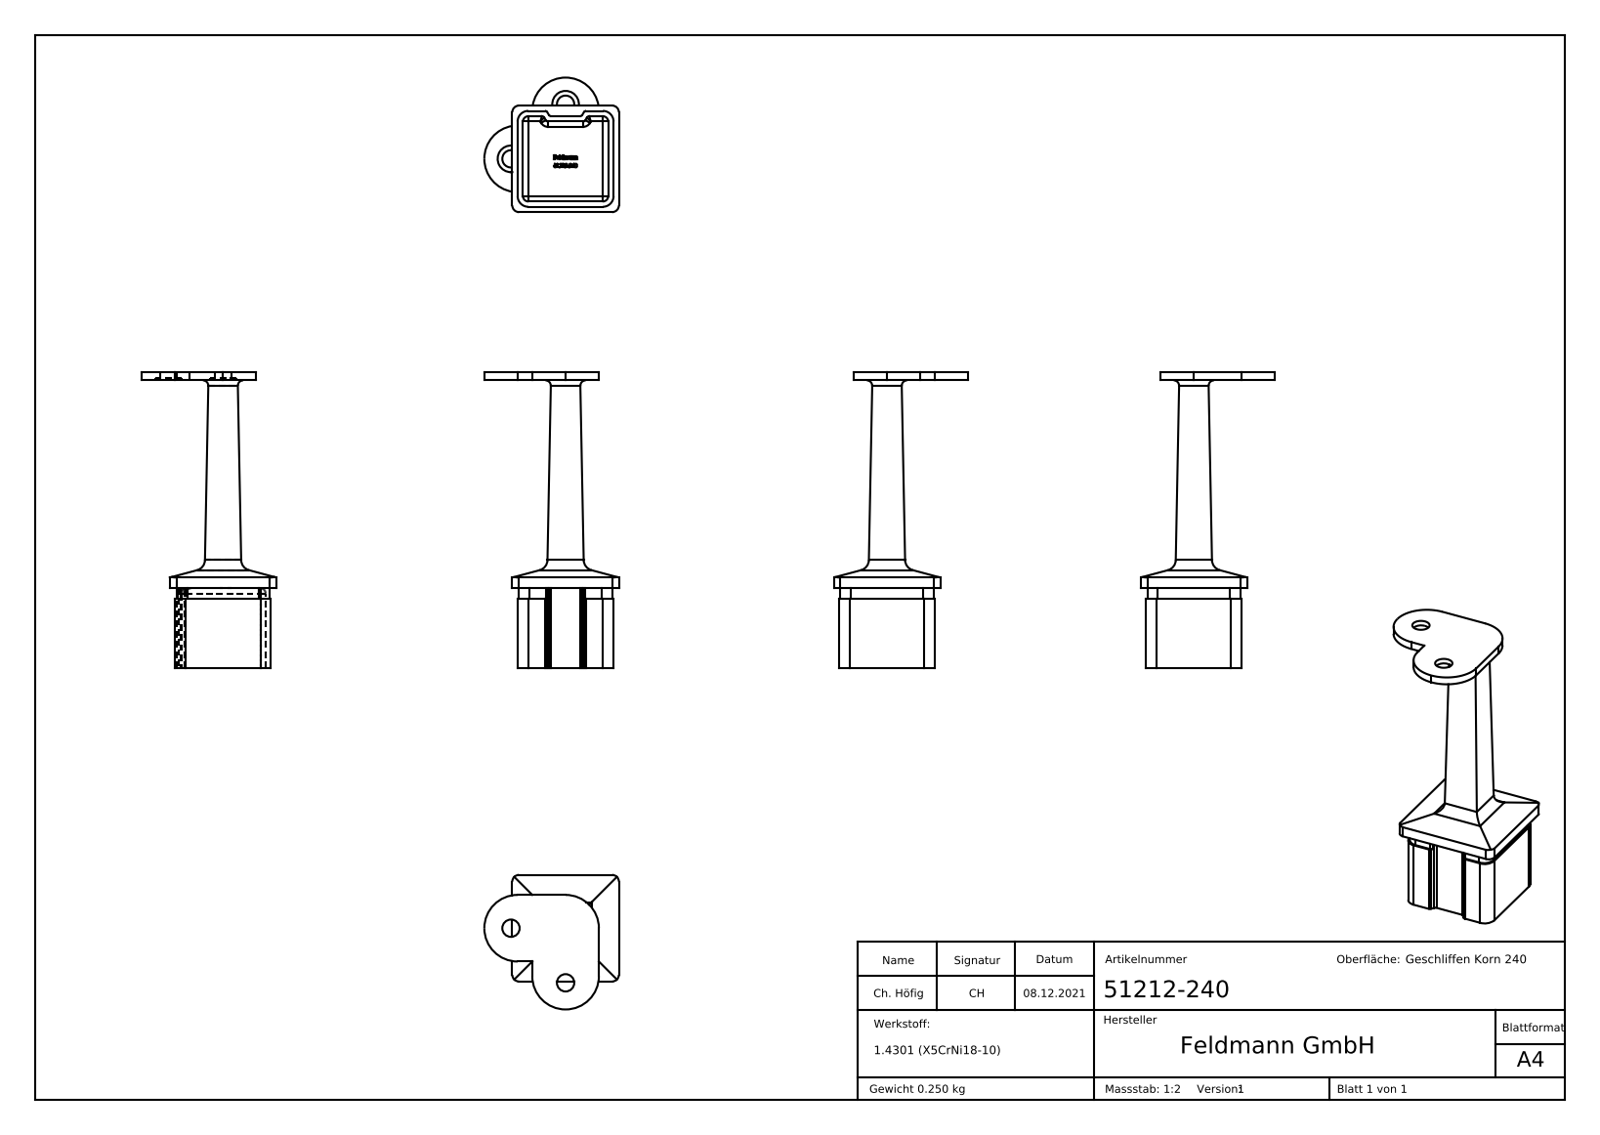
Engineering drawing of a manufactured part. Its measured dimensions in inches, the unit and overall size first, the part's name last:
Units: inches
Overall size (bounding box): 4.37 × 1.988 × 1.988
Round holes (diameter × count): ⌀0.256 ×2, ⌀0.394 ×2
Partial cylindrical surfaces — rounded edges, fillets, slot ends (radius × count): R0.079 ×15, R0.157 ×12, R0.039 ×10, R0.098 ×4, R0.492 ×3
Main face-to-face distances: 0.079, 1.339, 1.26, 1.417, 3.189, 3.071, 0.118, 0.157, 1.181, 1.496
Hole centre spacings: 1.141
Volume: 1.934 in³ · Surface area: 28.05 in²
Bodies: 1 solid, 316 faces (174 planar, 51 cylindrical, 91 other)
Part name (STEP PRODUCT): 51212-240
STEP written by: SolidWorks 2018 (CONFIG_CONTROL_DESIGN)
